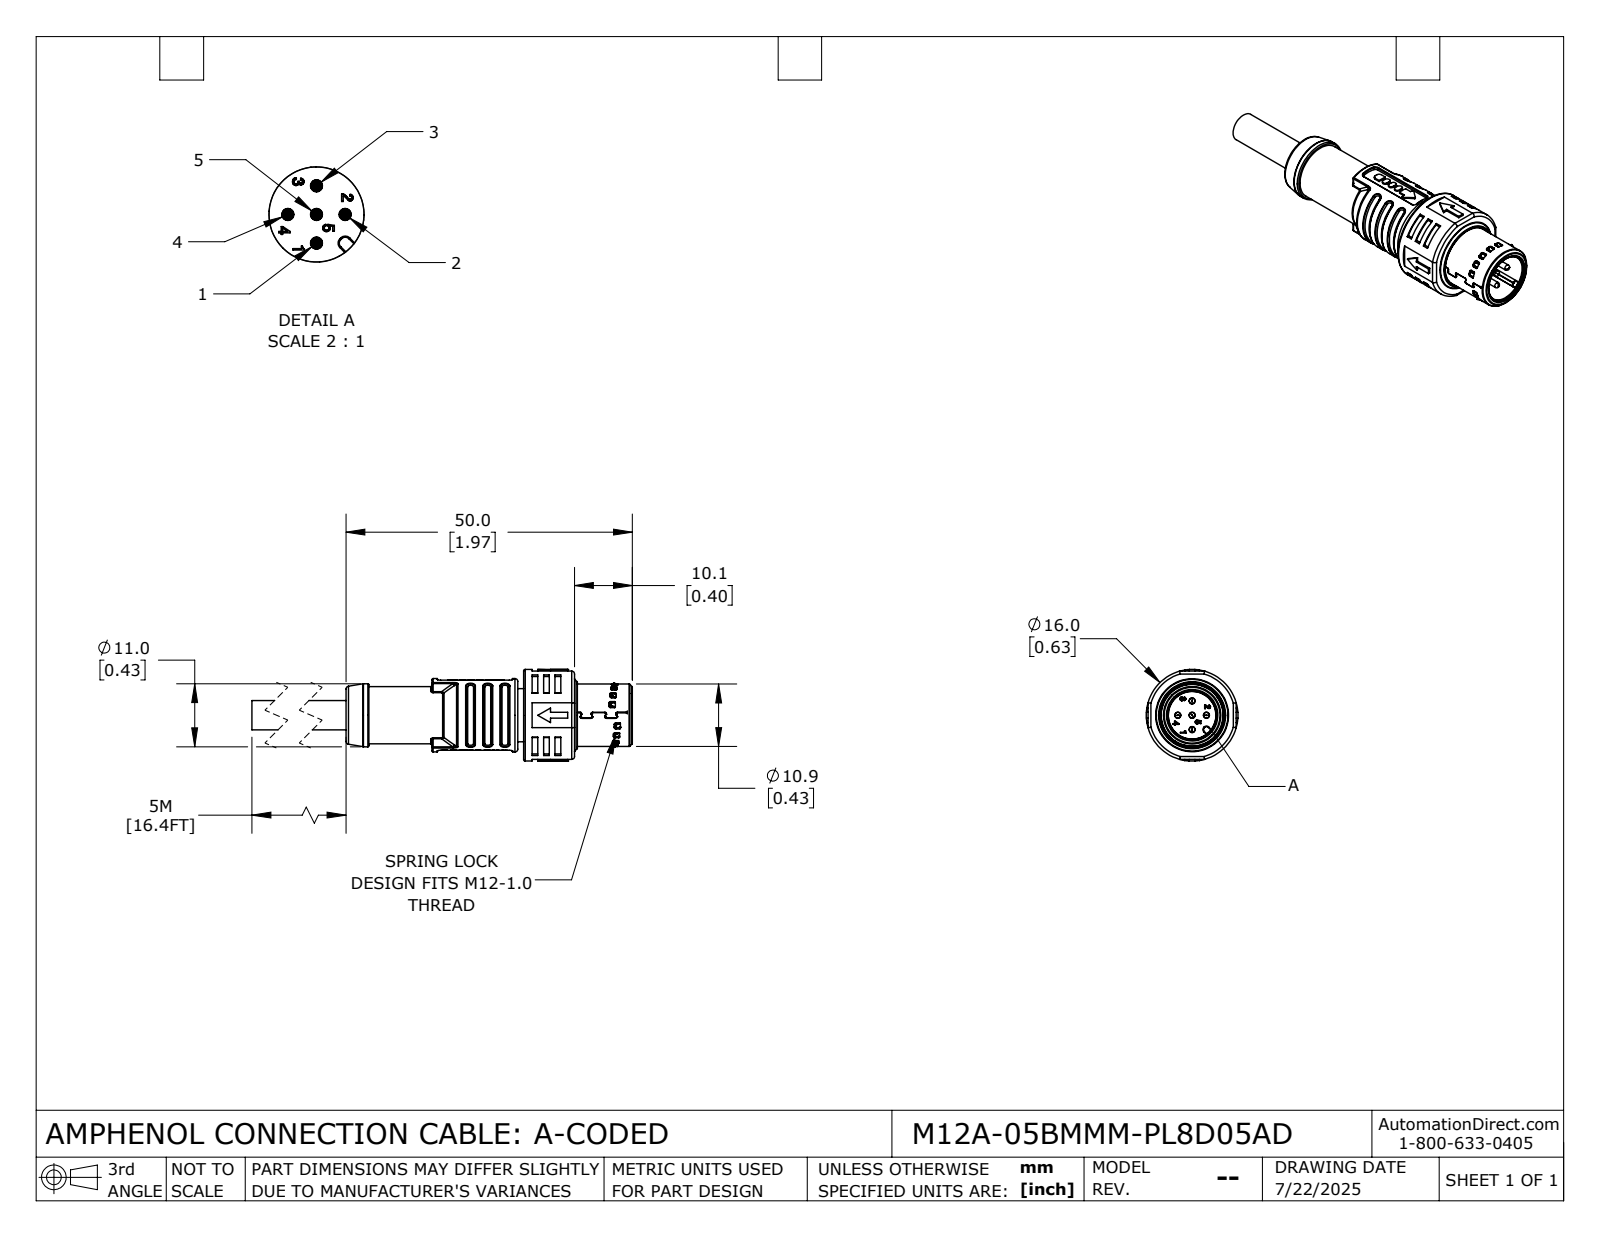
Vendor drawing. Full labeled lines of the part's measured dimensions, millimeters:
Part name (STEP PRODUCT): M12A-05BMMM-PL8D05AD
STEP written by: SolidWorks 2024 (CONFIG_CONTROL_DESIGN)
Units: millimetres
Bodies: 1 solid, 2230 faces (1085 planar, 648 cylindrical, 497 other)
Overall size (bounding box): 65 × 16 × 16
Volume: 5 076 mm³ · Surface area: 5 586 mm²
Round holes (diameter × count): ⌀1.05 ×5, ⌀8.3 ×1, ⌀9 ×1, ⌀10.15 ×1, ⌀10.5 ×1, ⌀10.9 ×1, ⌀11.5 ×1, ⌀11.8 ×1, ⌀14.2 ×1
Round bosses / shafts (diameter × count): ⌀1 ×5, ⌀16 ×1, ⌀14.1 ×1, ⌀12.8 ×1, ⌀12.4 ×1, ⌀11 ×1, ⌀10.45 ×1, ⌀10.4 ×1
Partial cylindrical surfaces — rounded edges, fillets, slot ends (radius × count): R0.2 ×114, R0.25 ×66, R0.3 ×64, R0.15 ×44, R0.5 ×38, R0.13 ×12, R0.7 ×11, R0.1 ×10
Main face-to-face distances: 1, 10.1, 8.9, 8.6, 2.5, 30, 1.5, 1.2, 32.5, 15.4
Hole centre spacings: 2.5, 3.54, 5
